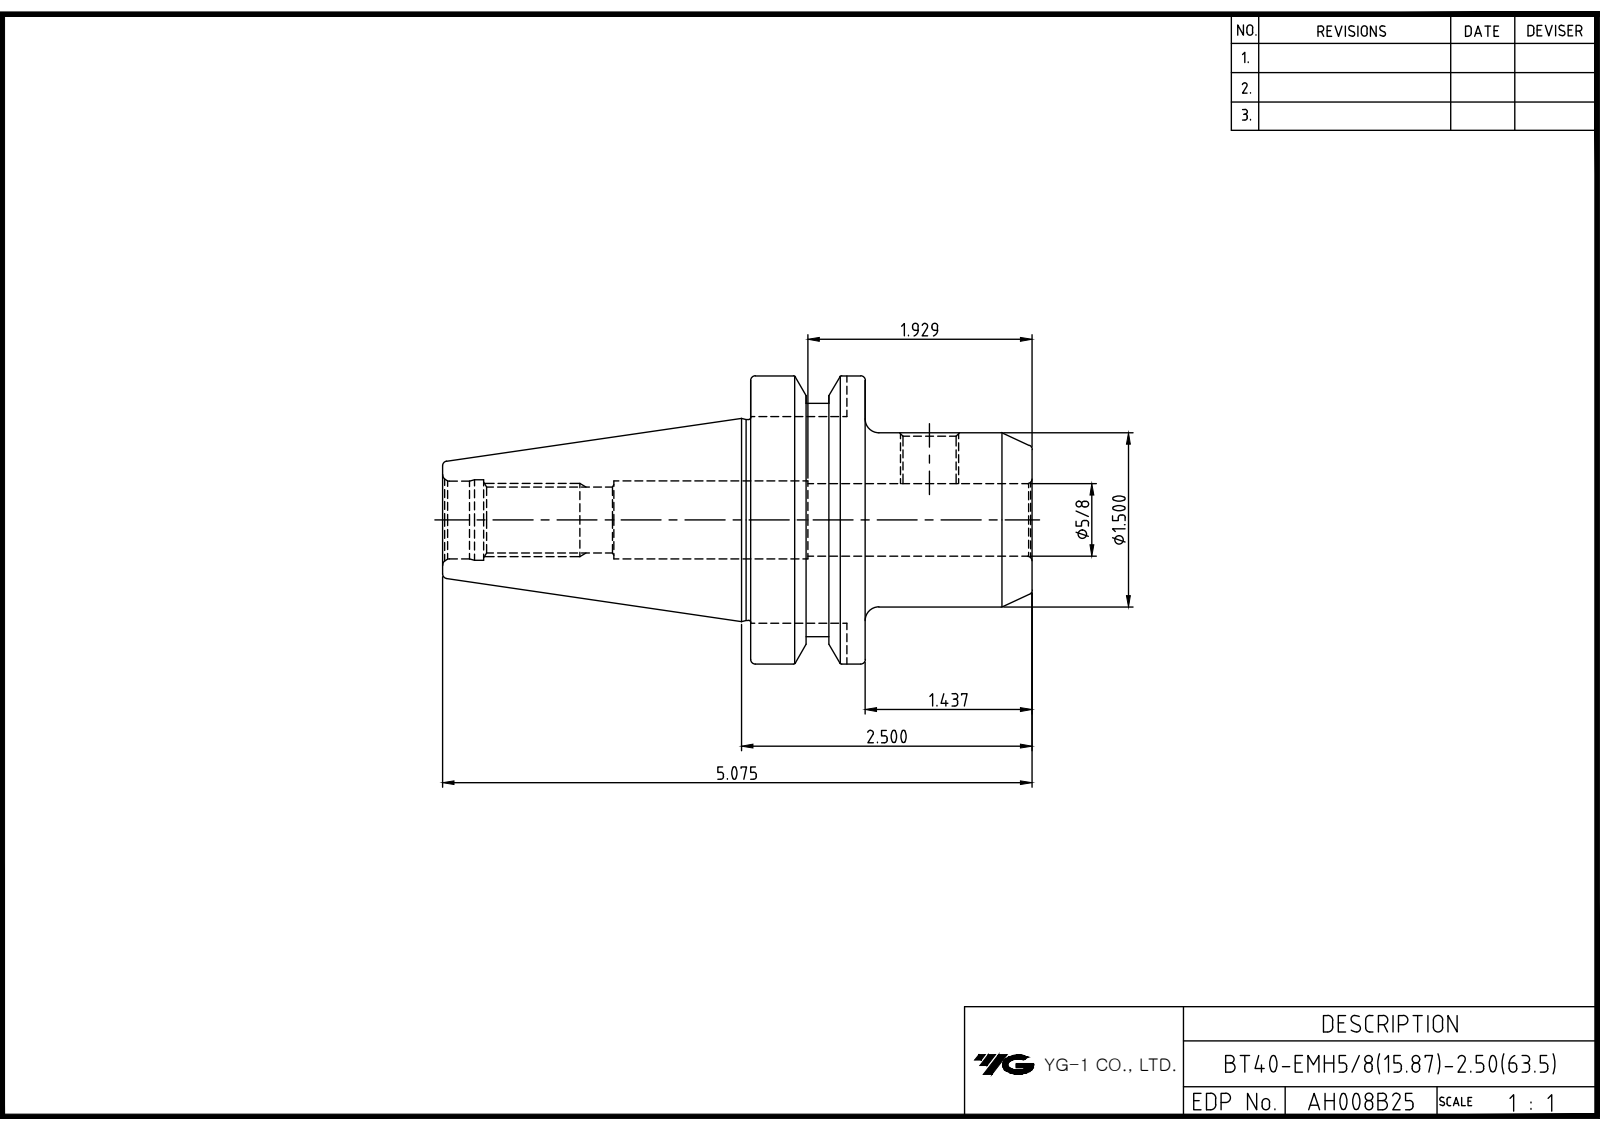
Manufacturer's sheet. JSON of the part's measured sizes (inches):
{"part_name": "LO-BT40-EMH15.875-63.5", "step_written_by": "Autodesk Inventor 2022 (AUTOMOTIVE_DESIGN)", "units": "inches", "bodies": {"solids": 1, "faces": 49, "planar": 17, "cylindrical": 15, "other": 17}, "overall_size": [5.075, 2.48, 2.48], "volume_in3": 9.02, "surface_area_in2": 44.82, "round_holes": [[0.446, 1], [0.545, 1], [0.625, 1], [0.669, 1], [0.672, 1], [0.693, 1]], "round_bosses_or_shafts": [[2.48, 1], [2.071, 1], [1.732, 1], [1.5, 1]], "partial_cylinders_radius": [[0.317, 1]], "face_to_face_distances": [0.984, 2.421, 1.437, 1.78, 0.634, 2.654, 3.638, 5.075, 3.327, 0.673]}
